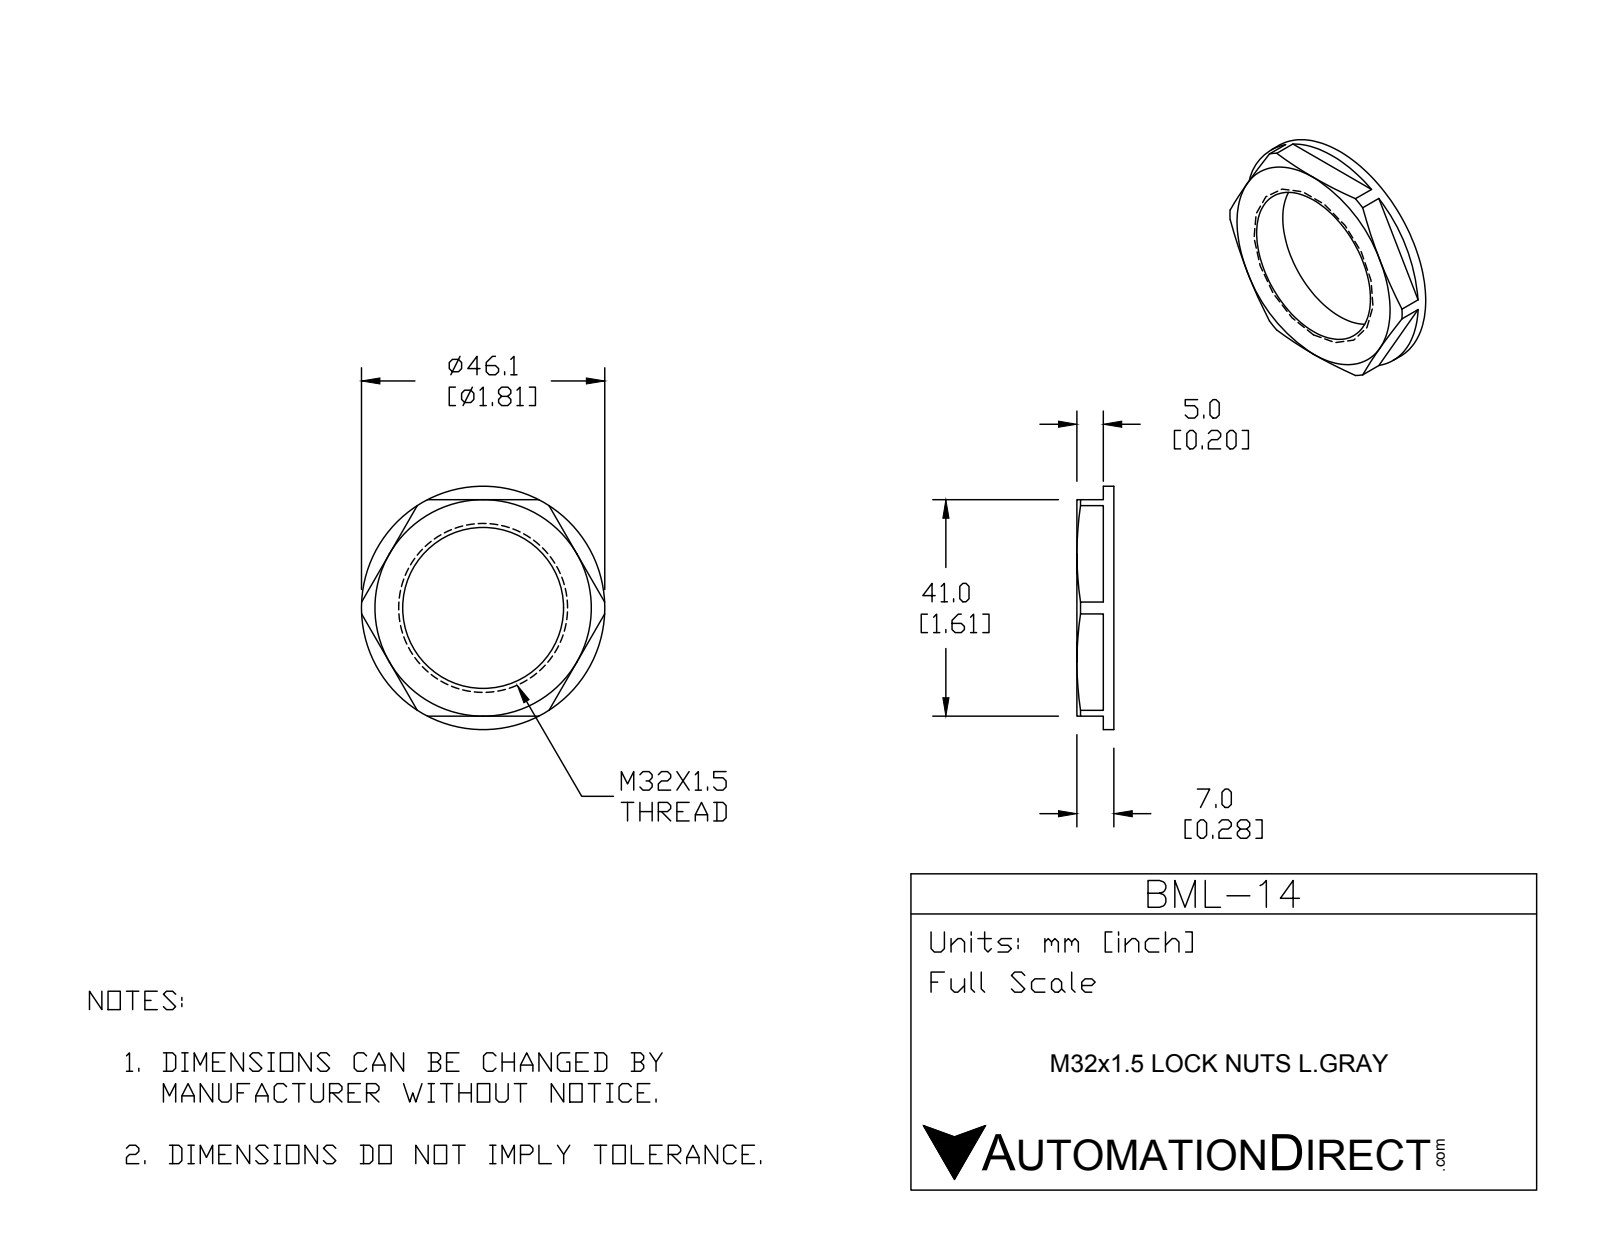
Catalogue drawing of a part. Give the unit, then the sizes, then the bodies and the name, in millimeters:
Units: millimetres
Overall size (bounding box): 46.1 × 46.1 × 7
Round holes (diameter × count): ⌀1.5 ×3, ⌀30.5 ×1
Round bosses / shafts (diameter × count): ⌀46.1 ×1
Main face-to-face distances: 7, 41, 2, 5, 1.7, 6.7
Hole centre spacings: 21.6, 37.41, 37.42
Volume: 5 449 mm³ · Surface area: 3 507 mm²
Bodies: 1 solid, 33 faces (17 planar, 10 cylindrical, 6 other)
Part name (STEP PRODUCT): BML-14
STEP written by: SolidWorks 2015 (CONFIG_CONTROL_DESIGN)
